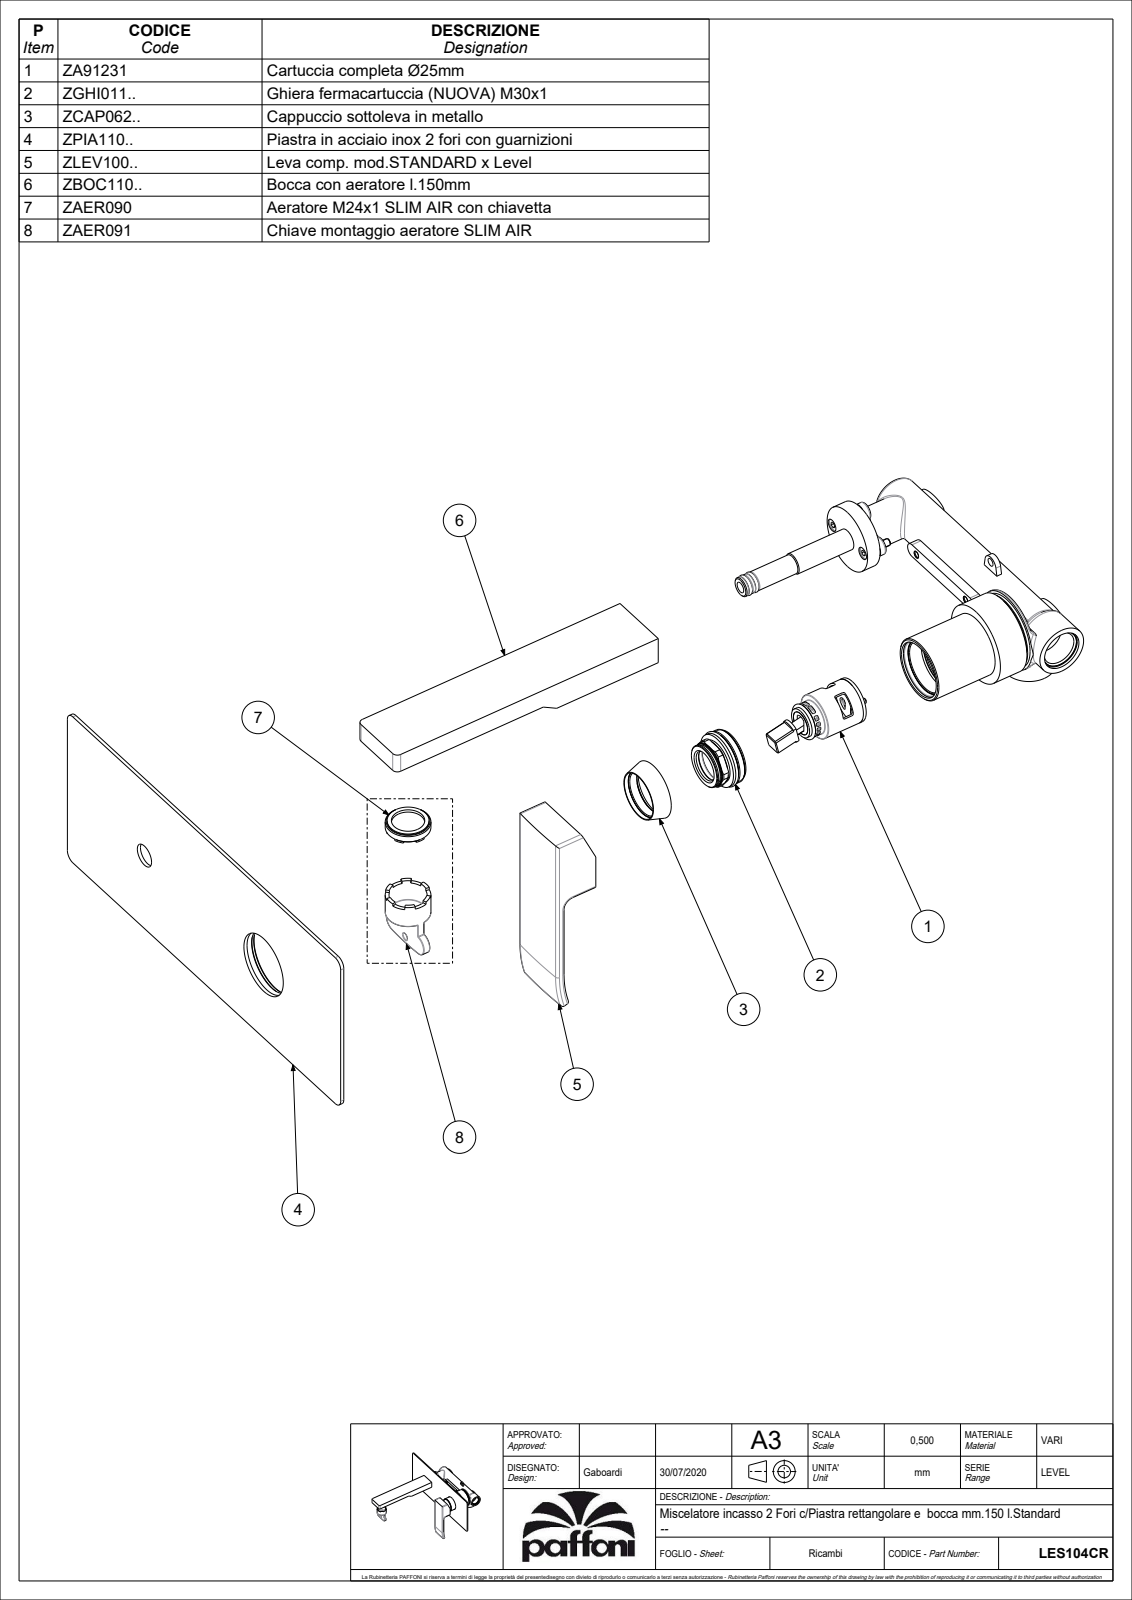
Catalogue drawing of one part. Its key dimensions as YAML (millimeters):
part_name: "LES104CR"
step_written_by: "CREO PARAMETRIC BY PTC INC, 2020044 (CONFIG_CONTROL_DESIGN)"
units: millimeters
bodies: {solids: 2, faces: 740, planar: 232, cylindrical: 279, other: 229}
overall_size: [250, 170, 141.36]
volume: 160477
surface_area: 101326
round_holes:
  - {diameter: 6, count: 2}
  - {diameter: 3, count: 1}
  - {diameter: 4.2, count: 1}
  - {diameter: 5.5, count: 1}
  - {diameter: 7.8, count: 1}
  - {diameter: 11, count: 1}
  - {diameter: 12, count: 1}
  - {diameter: 13, count: 1}
  - {diameter: 15, count: 1}
  - {diameter: 16.7, count: 1}
  - {diameter: 17, count: 1}
  - {diameter: 17.5, count: 1}
round_bosses_or_shafts:
  - {diameter: 35.2, count: 1}
  - {diameter: 30, count: 1}
  - {diameter: 27.7, count: 1}
  - {diameter: 25, count: 1}
  - {diameter: 23.8, count: 1}
  - {diameter: 22.5, count: 1}
  - {diameter: 19, count: 1}
  - {diameter: 18.5, count: 1}
partial_cylinders:
  - {radius: 0.5, count: 56}
  - {radius: 2, count: 16}
  - {radius: 1, count: 11}
  - {radius: 1.5, count: 8}
  - {radius: 5, count: 4}
  - {radius: 2.1, count: 2}
  - {radius: 2.5, count: 2}
  - {radius: 3, count: 2}
face_to_face_distances: [2, 35, 11.5, 5, 16.5, 109, 144, 74, 41.75, 58.25]
hole_center_spacings: [109, 161.88]
